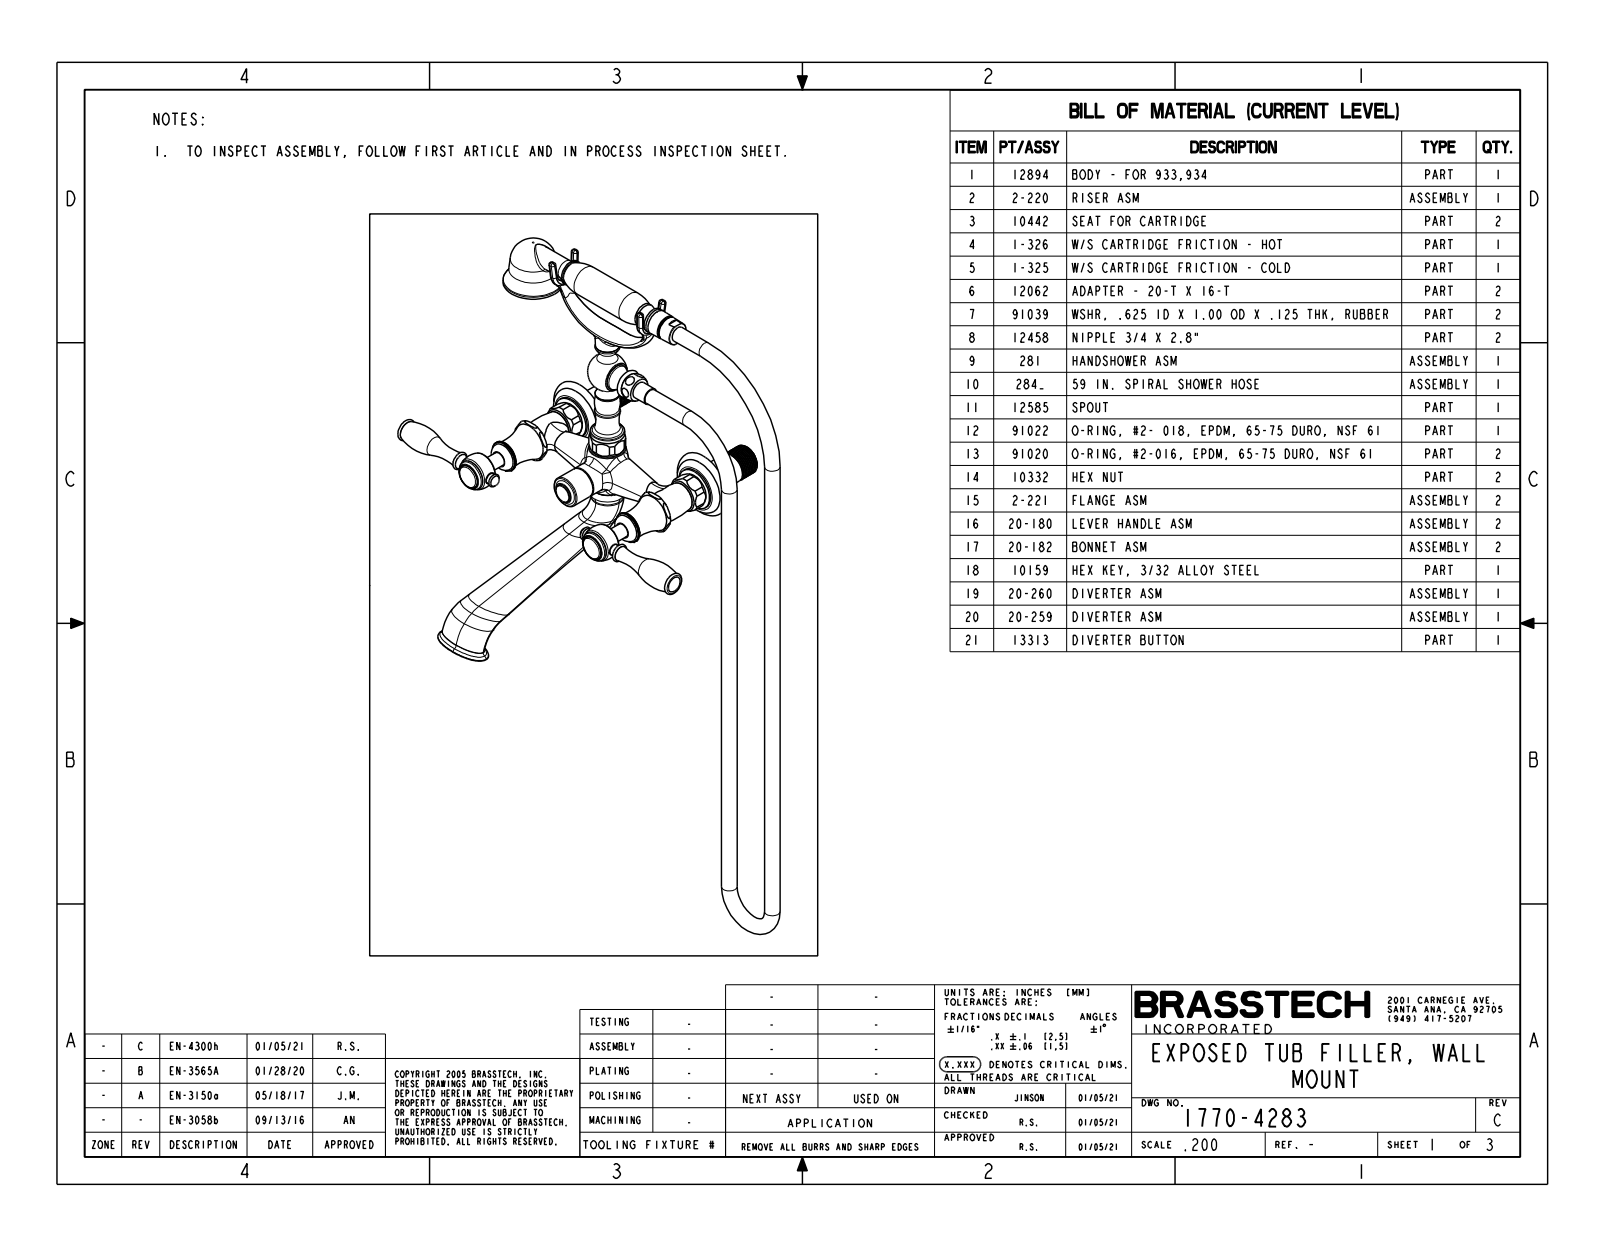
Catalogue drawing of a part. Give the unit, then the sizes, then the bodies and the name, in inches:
Units: inches
Overall size (bounding box): 23.86 × 14.919 × 9.14
Round holes (diameter × count): ⌀0.046 ×52, ⌀0.281 ×2, ⌀0.855 ×2, ⌀0.41 ×1
Round bosses / shafts (diameter × count): ⌀0.82 ×4, ⌀0.54 ×4, ⌀1.482 ×2, ⌀0.84 ×2, ⌀0.5 ×2, ⌀2.08 ×1, ⌀1.823 ×1, ⌀1.65 ×1
Partial cylindrical surfaces — rounded edges, fillets, slot ends (radius × count): R0.085 ×32, R0.637 ×3, R0.595 ×2, R0.405 ×1, R0.406 ×1, R0.45 ×1
Main face-to-face distances: 1.188, 3, 0.437, 2.283, 1.846, 0.58, 1.017, 1.266, 4.188, 1.812
Hole centre spacings: 1.002, 1.124, 0.185, 0.863, 1.227, 1.309, 1.369, 0.367
Volume: 52.46 in³ · Surface area: 279.9 in²
Bodies: 1 solid, 1151 faces (437 planar, 251 cylindrical, 463 other)
Part name (STEP PRODUCT): 12894
STEP written by: CREO PARAMETRIC BY PTC INC, 2018400 (CONFIG_CONTROL_DESIGN)
